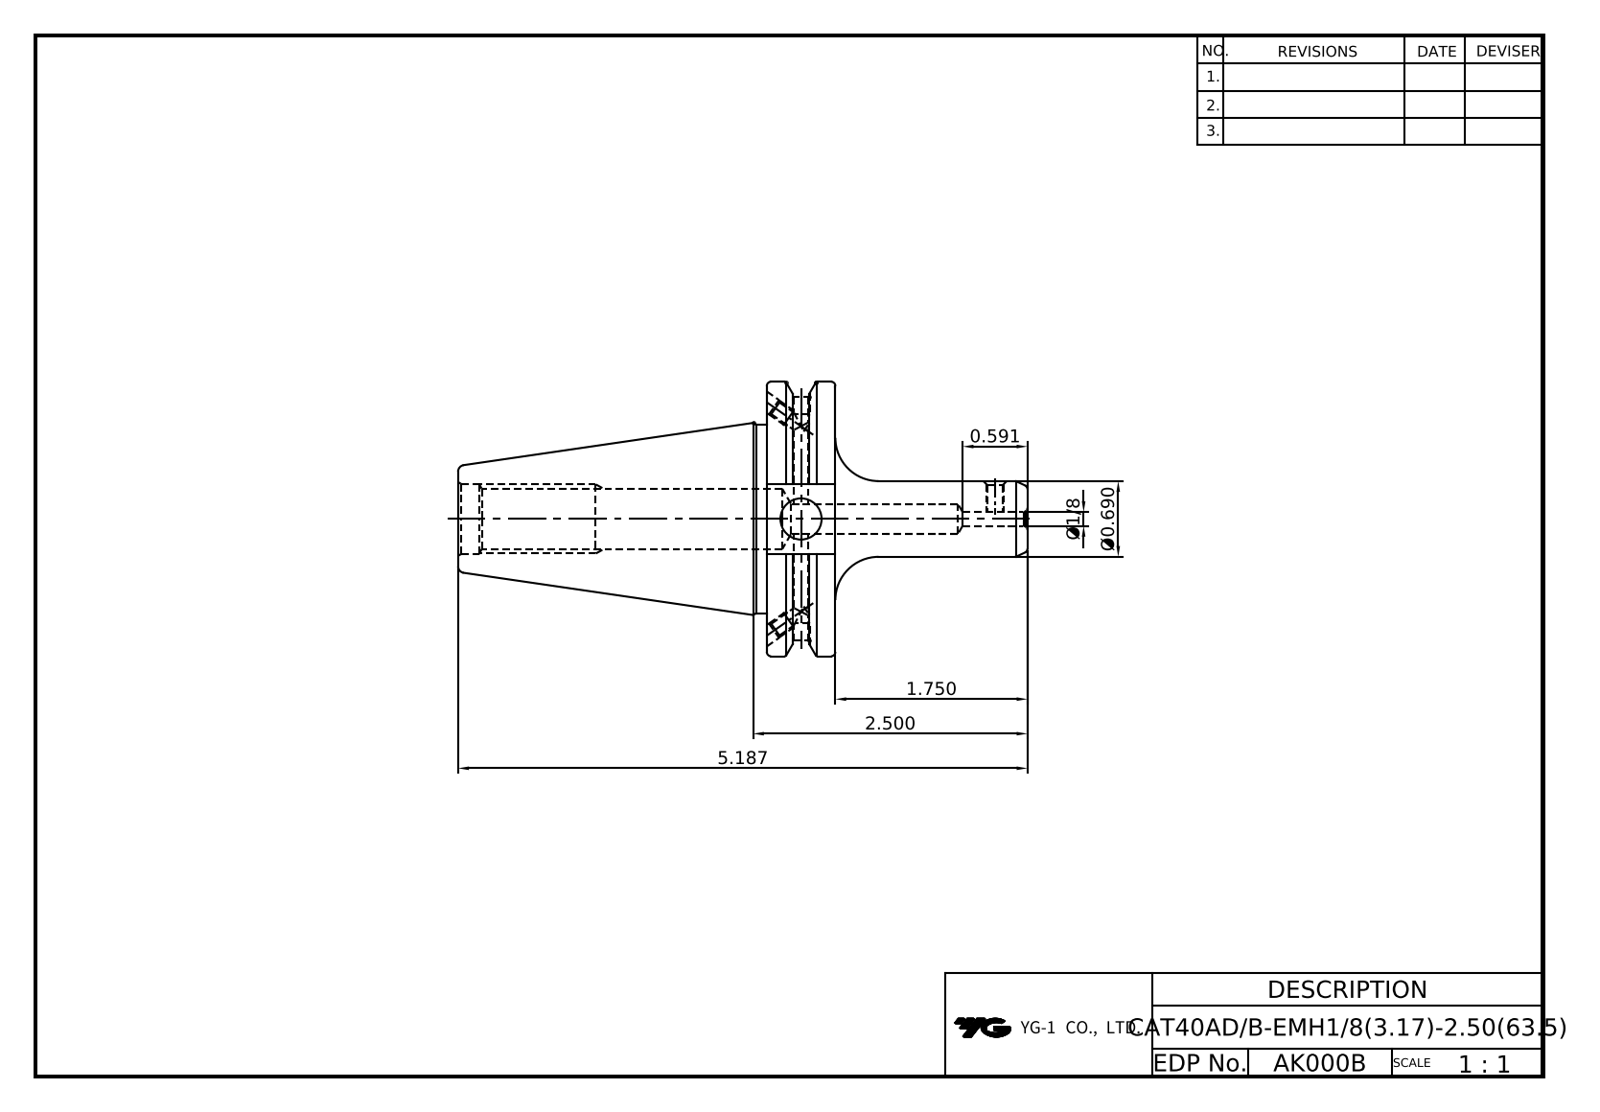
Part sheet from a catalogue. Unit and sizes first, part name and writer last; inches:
Units: inches
Overall size (bounding box): 5.187 × 2.5 × 2.405
Round holes (diameter × count): ⌀0.128 ×4, ⌀0.157 ×2, ⌀0.165 ×2, ⌀0.125 ×1, ⌀0.13 ×1, ⌀0.276 ×1, ⌀0.375 ×1, ⌀0.527 ×1, ⌀0.642 ×1
Round bosses / shafts (diameter × count): ⌀2.5 ×1, ⌀1.717 ×1, ⌀0.69 ×1
Partial cylindrical surfaces — rounded edges, fillets, slot ends (radius × count): R1.108 ×1
Main face-to-face distances: 0.625, 1.874, 0.645, 2.812, 3.437, 5.187, 2.375, 1.75, 3.05, 0.238
Volume: 6.824 in³ · Surface area: 37.17 in²
Bodies: 1 solid, 89 faces (35 planar, 28 cylindrical, 26 other)
Part name (STEP PRODUCT): LO-CAT40ADB-EMH3.175-63.5
STEP written by: Autodesk Inventor 2025 (AUTOMOTIVE_DESIGN)
